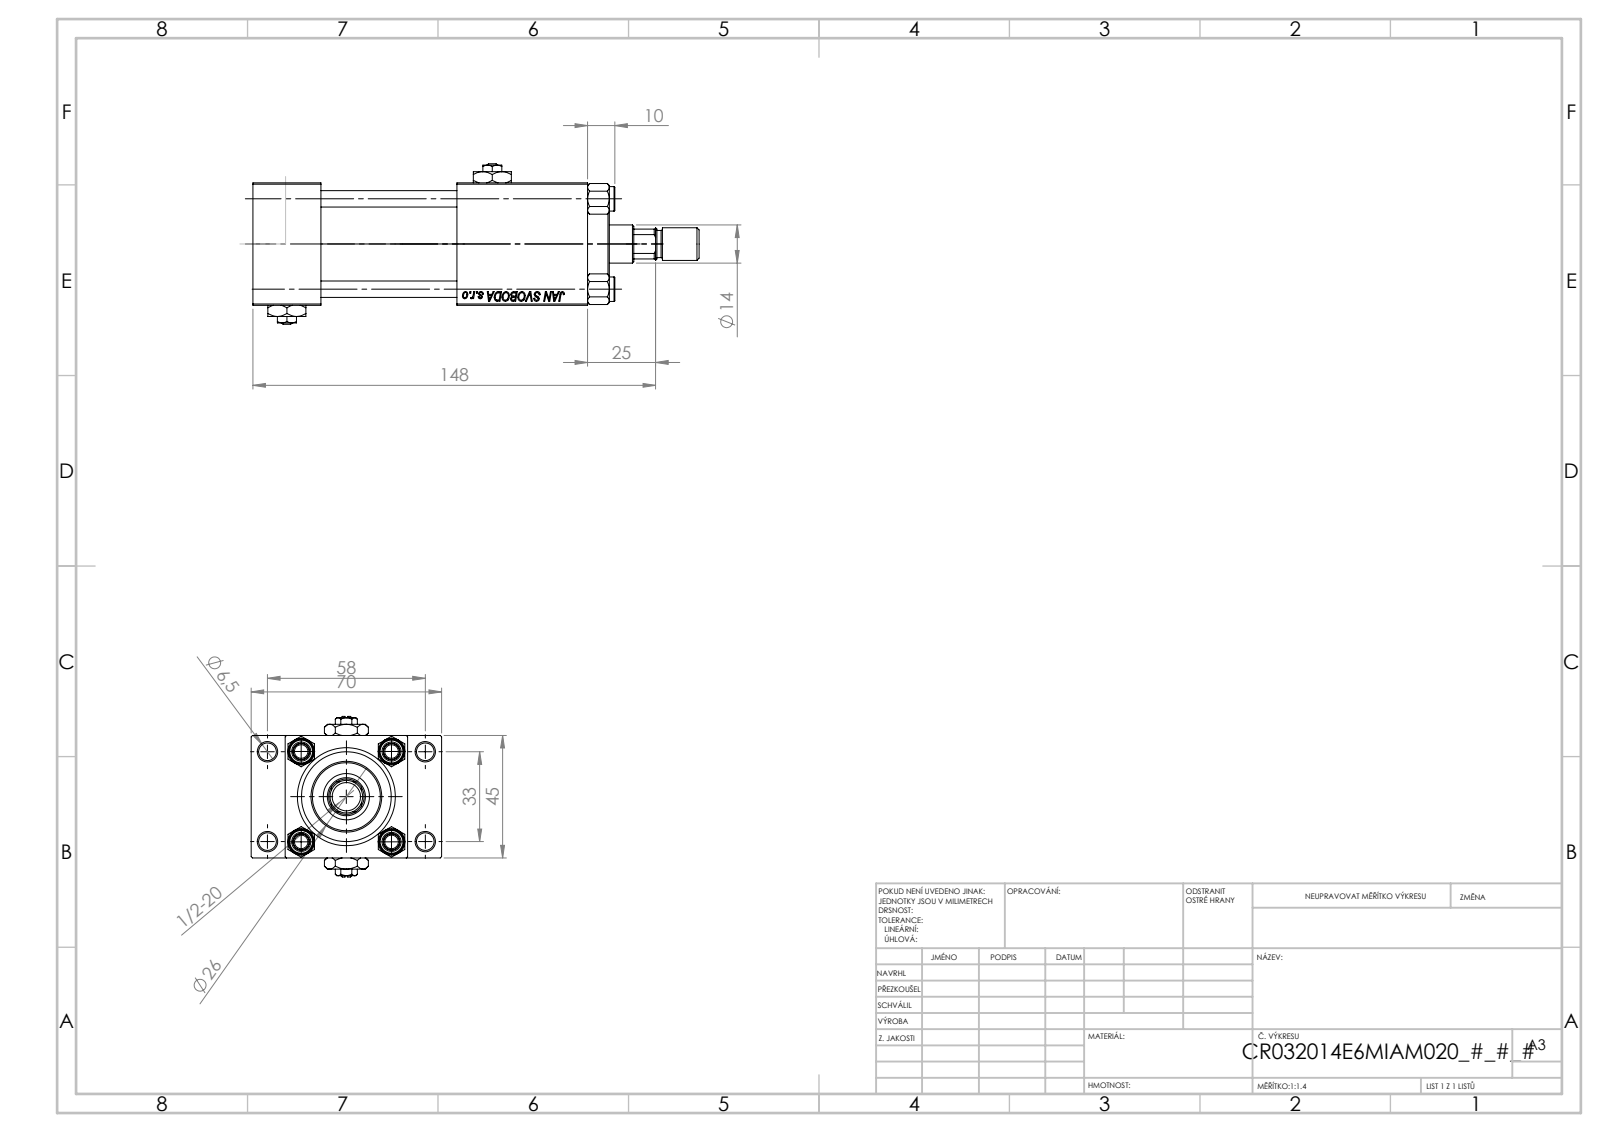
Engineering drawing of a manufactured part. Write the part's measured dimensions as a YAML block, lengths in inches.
part_name: "V215CR_TYCINKA_E; V215_VC_A; ROD_END_AH; V215CR_E_Body (+3 more)"
step_written_by: "SolidWorks 2019 (CONFIG_CONTROL_DESIGN)"
units: inches
bodies: {solids: 14, faces: 1243, planar: 546, cylindrical: 97, other: 600}
overall_size: [6.457, 2.756, 2.323]
volume: 13.5
surface_area: 122.2
round_holes:
  - {diameter: 0.256, count: 5}
  - {diameter: 0.236, count: 4}
  - {diameter: 0.276, count: 3}
  - {diameter: 0.518, count: 3}
  - {diameter: 0.787, count: 3}
  - {diameter: 0.551, count: 1}
  - {diameter: 0.669, count: 1}
  - {diameter: 0.945, count: 1}
  - {diameter: 1.26, count: 1}
  - {diameter: 1.299, count: 1}
round_bosses_or_shafts:
  - {diameter: 0.354, count: 4}
  - {diameter: 1.496, count: 1}
  - {diameter: 1.024, count: 1}
  - {diameter: 0.472, count: 1}
  - {diameter: 0.394, count: 1}
partial_cylinders:
  - {radius: 0.256, count: 1}
face_to_face_distances: [1.772, 0.984, 0.492, 2.264, 4.843, 3.858, 1.969, 2.953, 1.89, 3.713]
hole_center_spacings: [0.488, 0.924, 1.307, 1.314, 1.392, 1.795, 2.219, 1.299]
